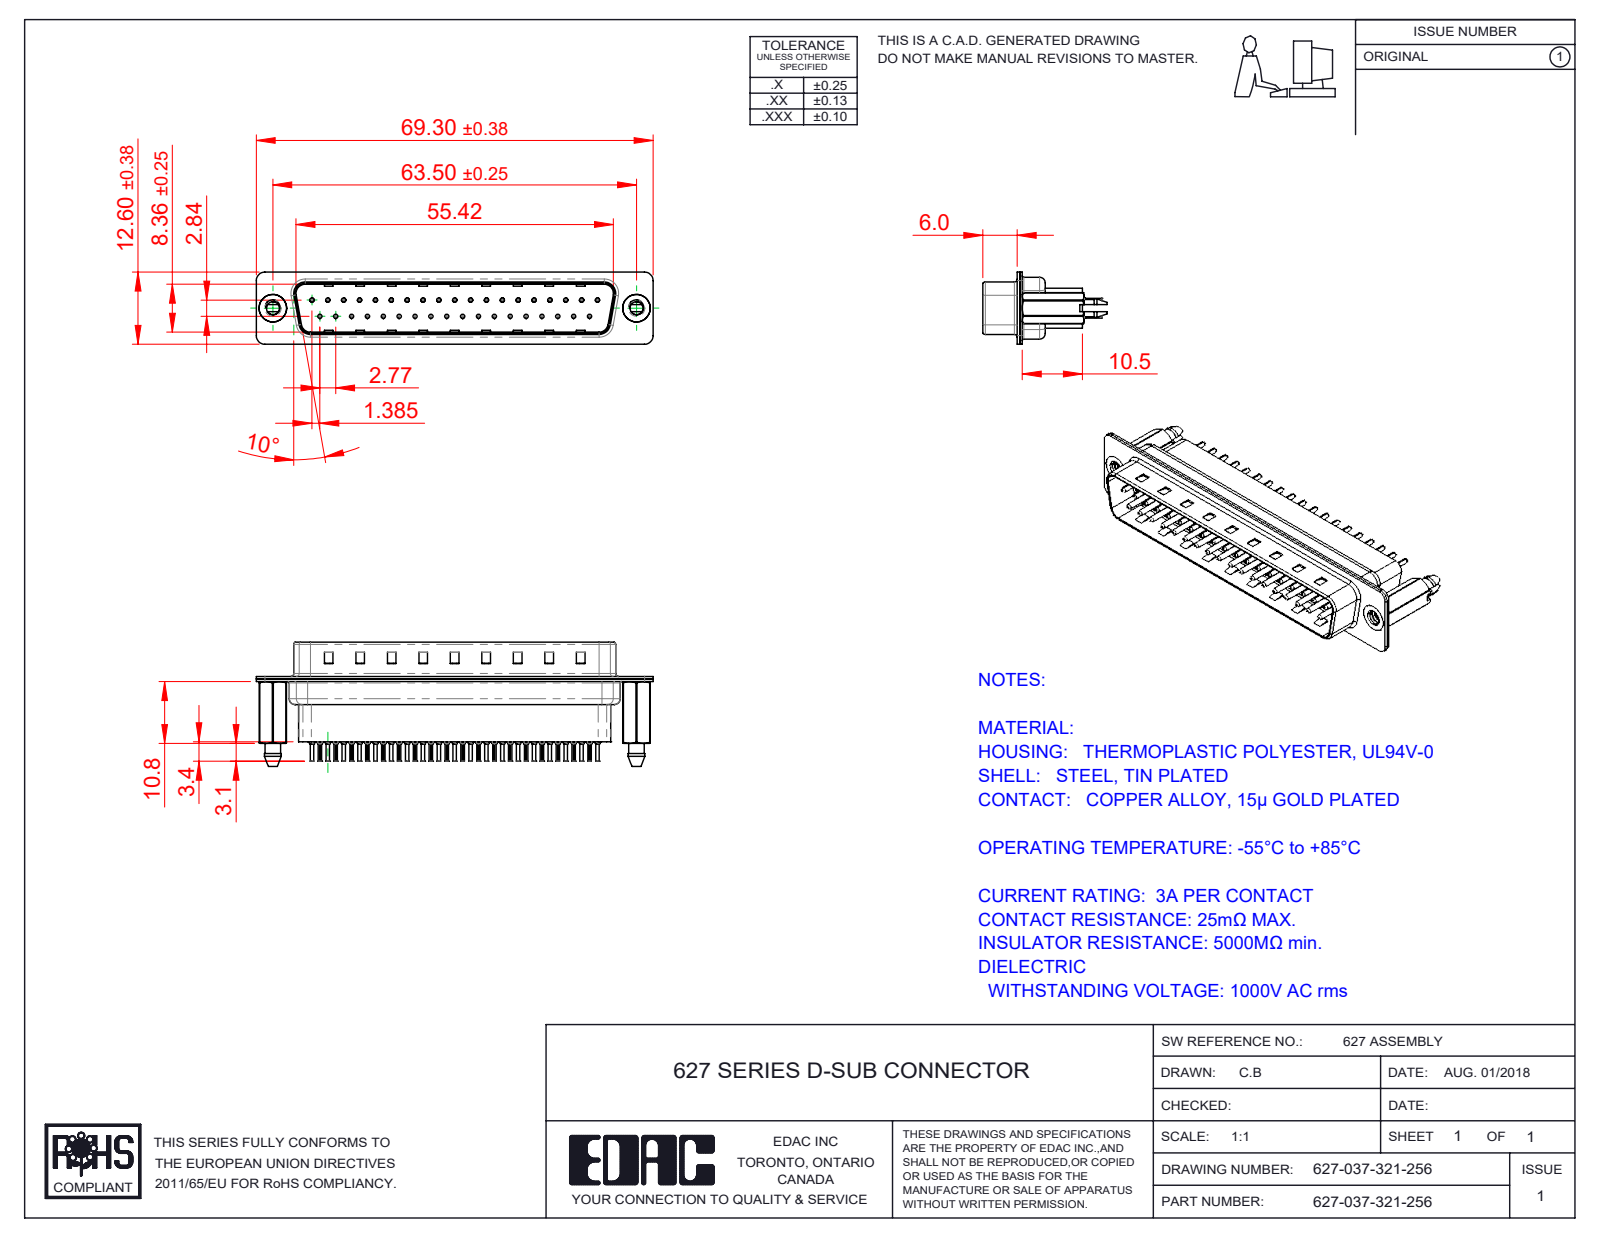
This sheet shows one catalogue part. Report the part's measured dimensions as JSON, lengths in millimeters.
{"part_name": "627 Shell Front_37 Contacts; 627 Contact Row 1_21H; 627 4-40 Threaded Boardlock_HP; 627-037-321-056 (+3 more)", "step_written_by": "SolidWorks 2020 (CONFIG_CONTROL_DESIGN)", "units": "millimeters", "bodies": {"solids": 42, "faces": 4152, "planar": 1123, "cylindrical": 1578, "other": 1451}, "overall_size": [69.3, 21.7, 12.6], "volume_mm3": 5558, "surface_area_mm2": 14141, "round_holes": [[0.2, 37], [0.35, 37], [1.1, 37], [1.6, 37], [2.26, 2], [4, 2], [4.8, 2]], "round_bosses_or_shafts": [[2, 37], [1.5, 37], [0.75, 37], [0.6, 37], [4.9, 2]], "partial_cylinders_radius": [[0.1, 74], [1.5, 18], [2, 12], [1.6, 10], [0.5, 8], [0.25, 4], [0.6, 4], [0.65, 4]], "face_to_face_distances": [0.4, 0.82, 9.58, 0.45, 0.68, 7.68, 1.5, 1.08, 8.08, 8.76], "hole_center_spacings": [3.16, 2.77, 5.54, 8.31, 5.04, 10.1, 11.08, 12.78]}
